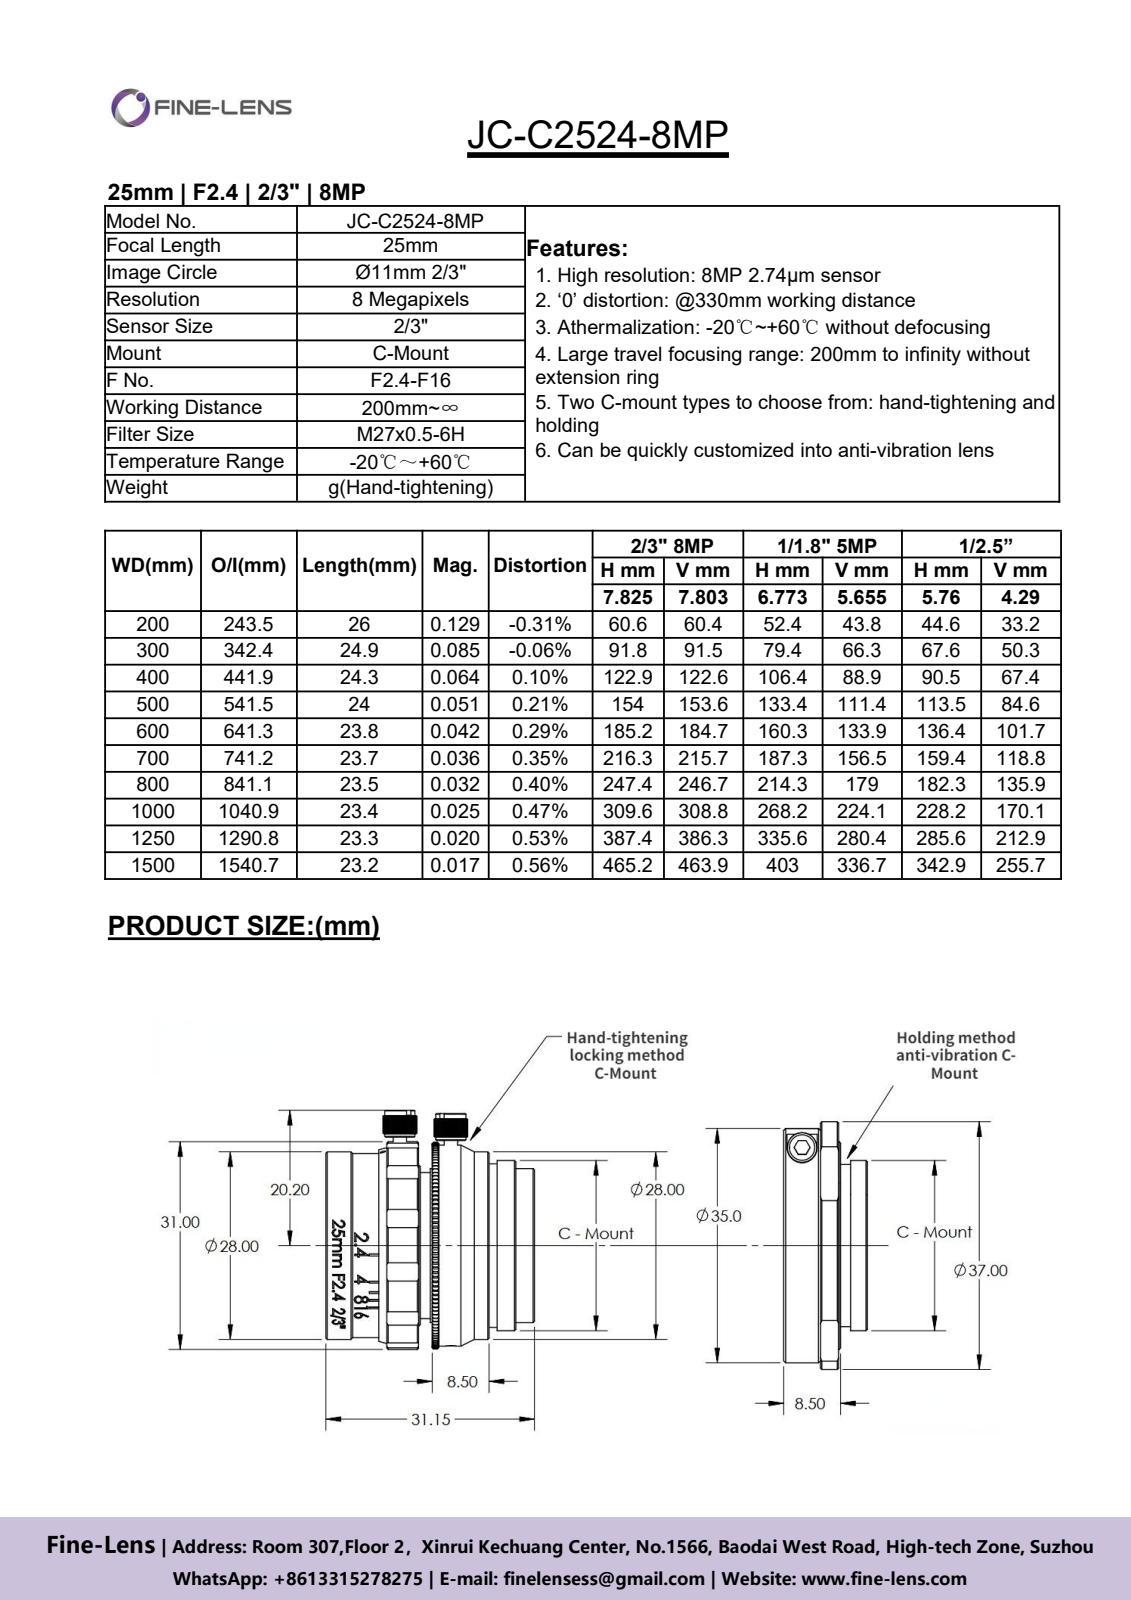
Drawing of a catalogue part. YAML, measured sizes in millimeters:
part_name: "1101"
step_written_by: "SolidWorks 2016 (CONFIG_CONTROL_DESIGN)"
units: millimeters
bodies: {solids: 4, faces: 1108, planar: 412, cylindrical: 240, other: 456}
overall_size: [31.15, 31, 31]
volume: 18597
surface_area: 8550
round_holes:
  - {diameter: 1.6, count: 2}
  - {diameter: 0.8, count: 1}
  - {diameter: 22.4, count: 1}
  - {diameter: 23, count: 1}
  - {diameter: 24.6, count: 1}
  - {diameter: 27.6, count: 1}
  - {diameter: 29, count: 1}
round_bosses_or_shafts:
  - {diameter: 30, count: 1}
  - {diameter: 28, count: 1}
  - {diameter: 27.5, count: 1}
  - {diameter: 26.6, count: 1}
  - {diameter: 25.4, count: 1}
  - {diameter: 24.4, count: 1}
  - {diameter: 24, count: 1}
  - {diameter: 23.2, count: 1}
partial_cylinders:
  - {radius: 2.5, count: 12}
  - {radius: 1, count: 1}
  - {radius: 13.77, count: 1}
  - {radius: 14.02, count: 1}
  - {radius: 15.4, count: 1}
  - {radius: 15.5, count: 1}
face_to_face_distances: [15.4, 31.15, 2.55, 12.85, 18.3, 15.75, 8.5, 1, 13.85, 1.55]
hole_center_spacings: [7.15]
